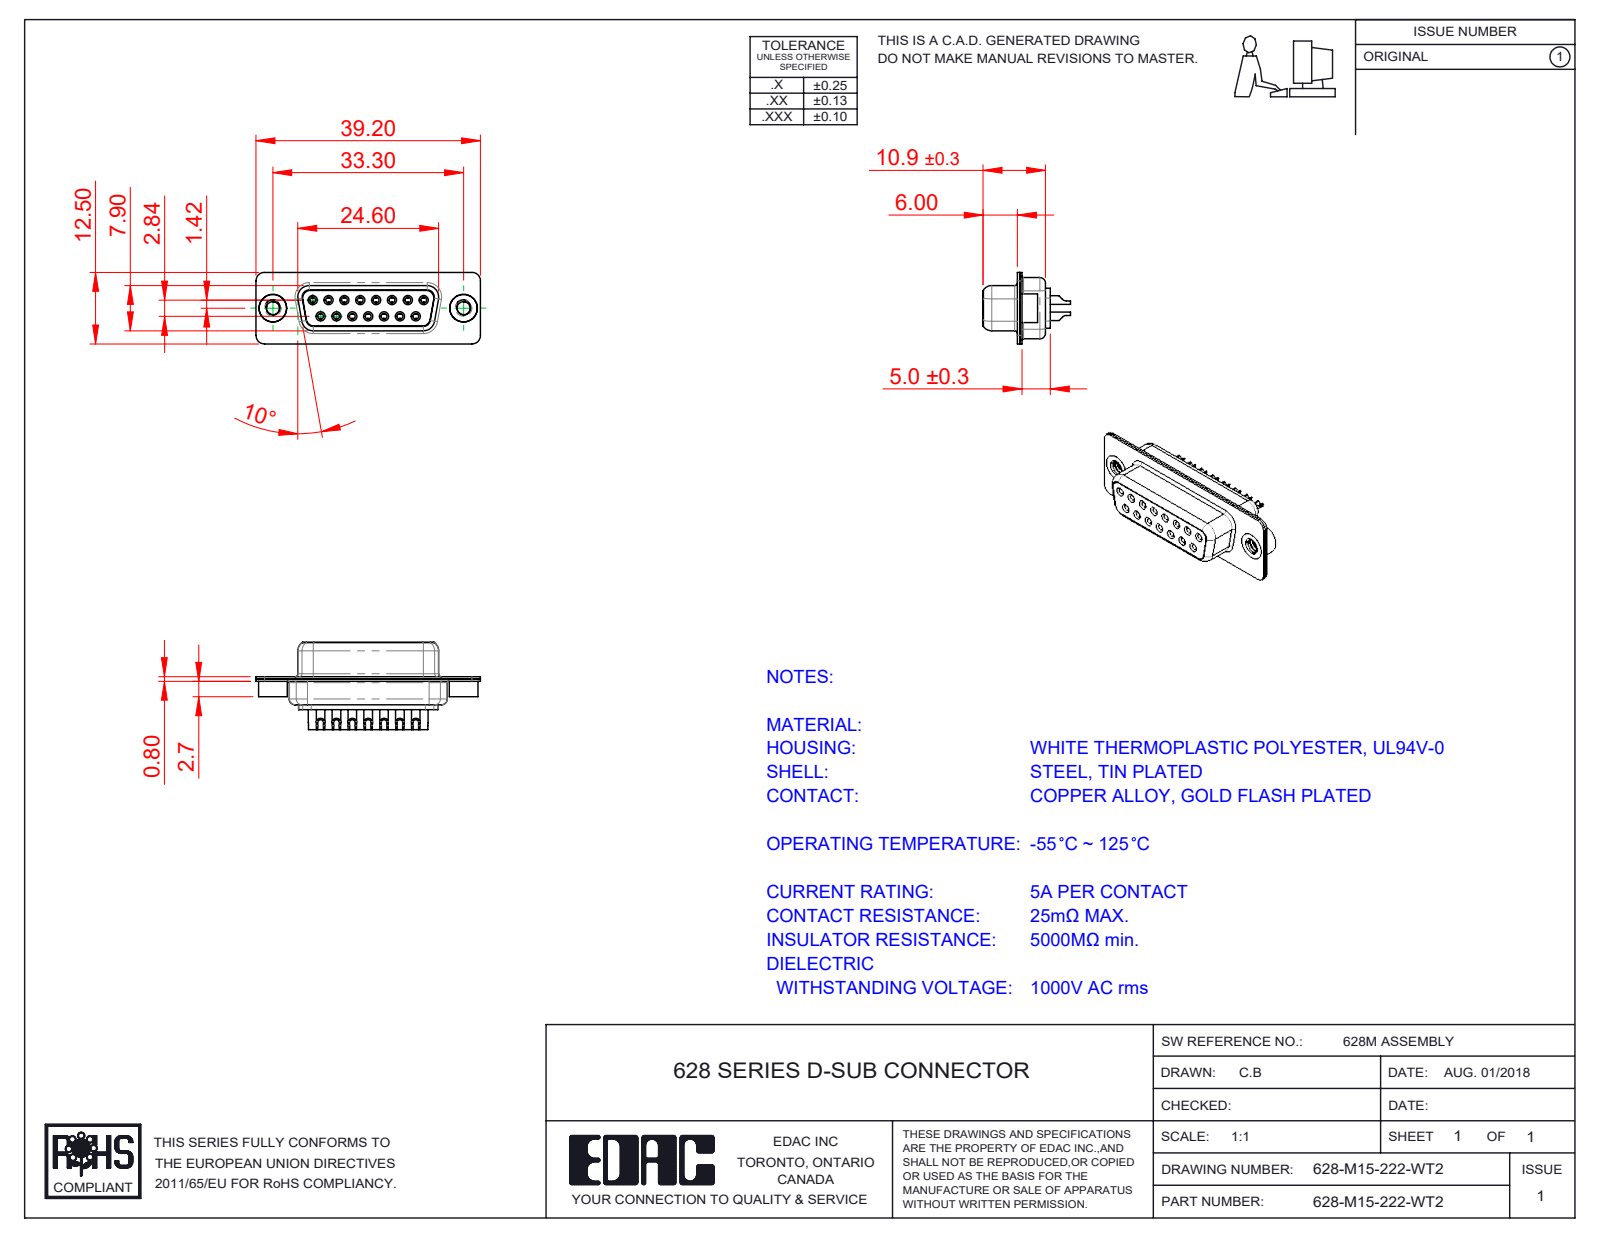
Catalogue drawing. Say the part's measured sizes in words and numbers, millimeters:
The part is named "628M Shell Rear_15 Contacts; 628M Housing_15 Contacts; 628M Contact Row 1_22; 628M 4-40 Threaded Rivet (+3 more)". Its 3-D file was written by "SolidWorks 2020 (CONFIG_CONTROL_DESIGN)". It is 20 solids with 1105 faces: 323 planar, 452 cylindrical and 330 other. Overall it measures 39.2 by 15.25 by 12.5 millimeters. Its volume is 2 494 cubic millimeters and its surface area 6 329 square millimeters. Round holes: 15 of diameter 1, 15 of diameter 1.1, 15 of diameter 1.7, 15 of diameter 1.8, 15 of diameter 2, 2 of diameter 2.26, 2 of diameter 4, 2 of diameter 4.8. Round bosses or shafts: 15 of diameter 2.2, 15 of diameter 1.6, 15 of diameter 1.5, 2 of diameter 5, 2 of diameter 4.9. Partial cylindrical surfaces (rounded edges, fillets, slot ends): 16 of radius 1.5, 12 of radius 2, 8 of radius 1.35, 8 of radius 1.6, 6 of radius 1, 4 of radius 0.25, 4 of radius 0.5, 4 of radius 0.6. The main face-to-face distances are 0.4, 1.4, 0.45, 8.45, 8.9, 1.8, 7.05, 1, 0.85, 1.85. The hole center spacings are 3.16, 2.77, 5.54, 8.31, 11.08, 5.03, 5.04, 7.48.
